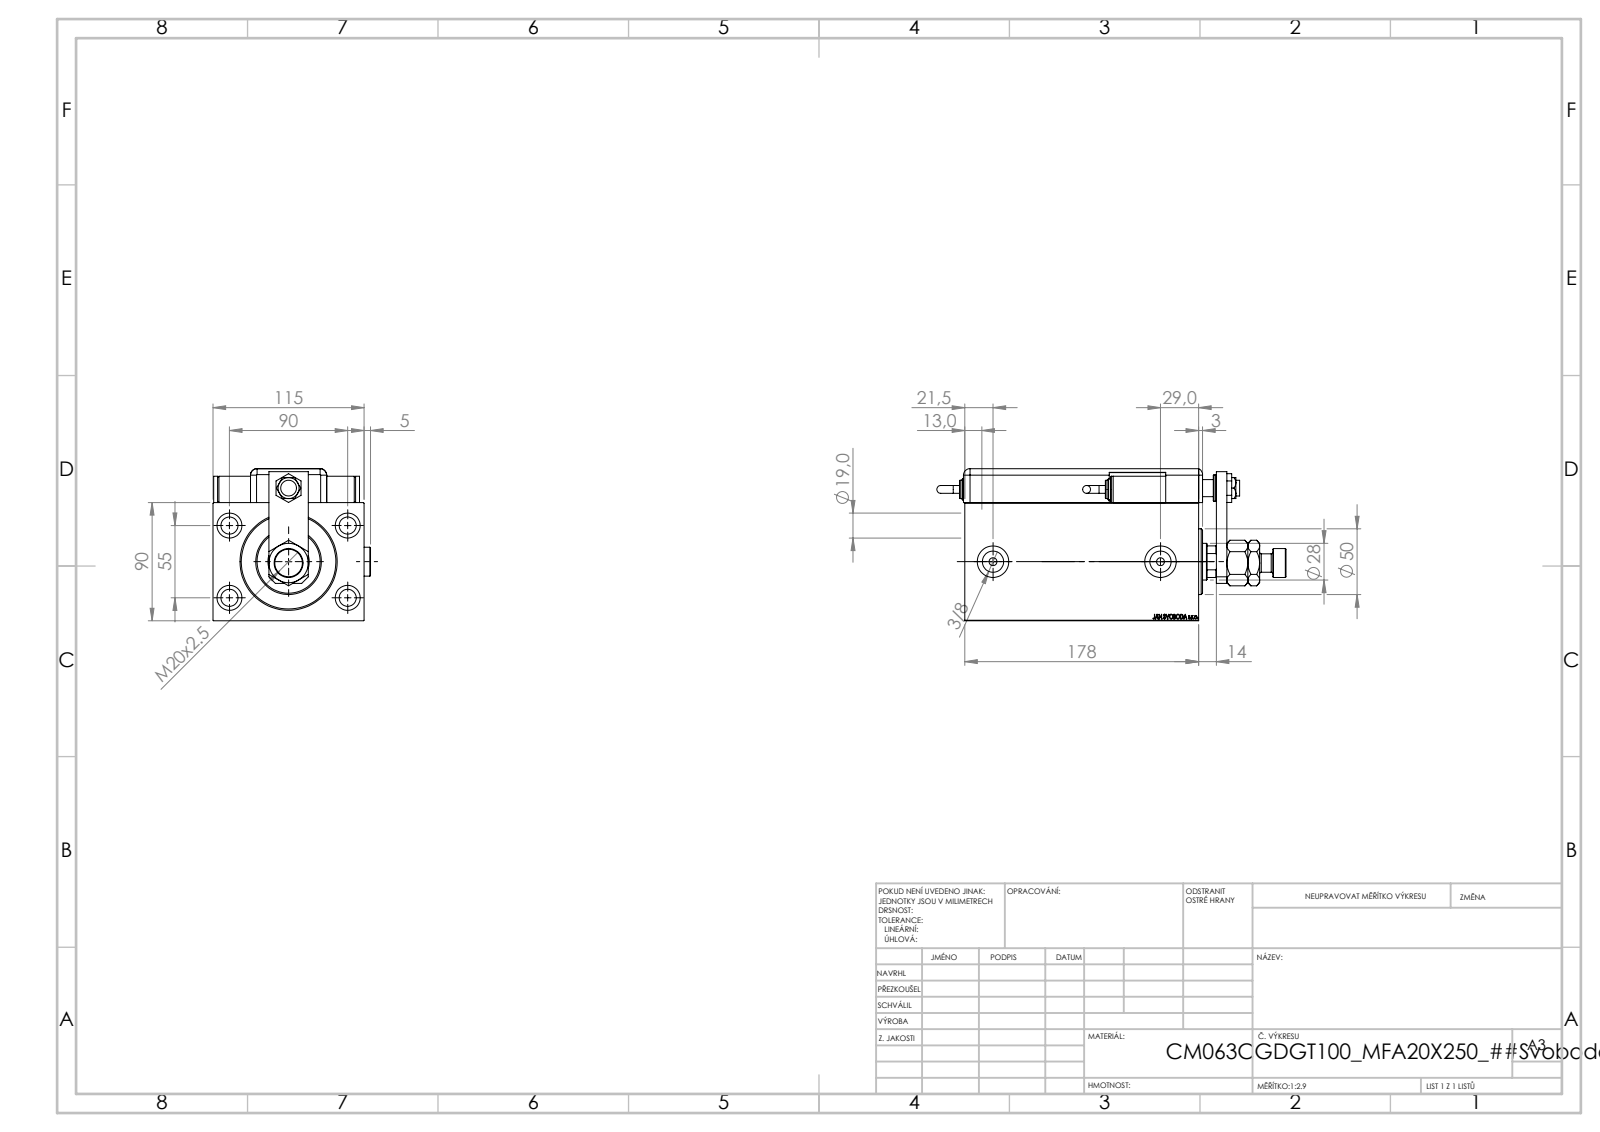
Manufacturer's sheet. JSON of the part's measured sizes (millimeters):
{"part_name": "ZARAZKA_Q; NUT_D13; MAGNETIC SWITCH Q; SWITCH_Q_FRONT_BACK (+7 more)", "step_written_by": "SolidWorks 2019 (CONFIG_CONTROL_DESIGN)", "units": "millimeters", "bodies": {"solids": 16, "faces": 1355, "planar": 665, "cylindrical": 137, "other": 553}, "overall_size": [265.76, 119.9, 115.8], "volume_mm3": 1683000, "surface_area_mm2": 281286, "round_holes": [[13, 5], [19, 4], [4, 2], [6, 2], [8, 2], [16.17, 2], [24, 2], [12, 1], [14, 1], [18.5, 1], [20, 1], [28, 1]], "round_bosses_or_shafts": [[22, 3], [20, 3], [14, 3], [16, 2], [6, 2], [50, 1]], "partial_cylinders_radius": [[5, 9], [10, 1], [13.5, 1]], "face_to_face_distances": [90, 3, 115, 178, 25.8, 115.8, 28.5, 112.8, 22.8, 17.5], "hole_center_spacings": [52.74, 53.27, 52.22, 55, 90, 94.85, 105.48, 1]}
